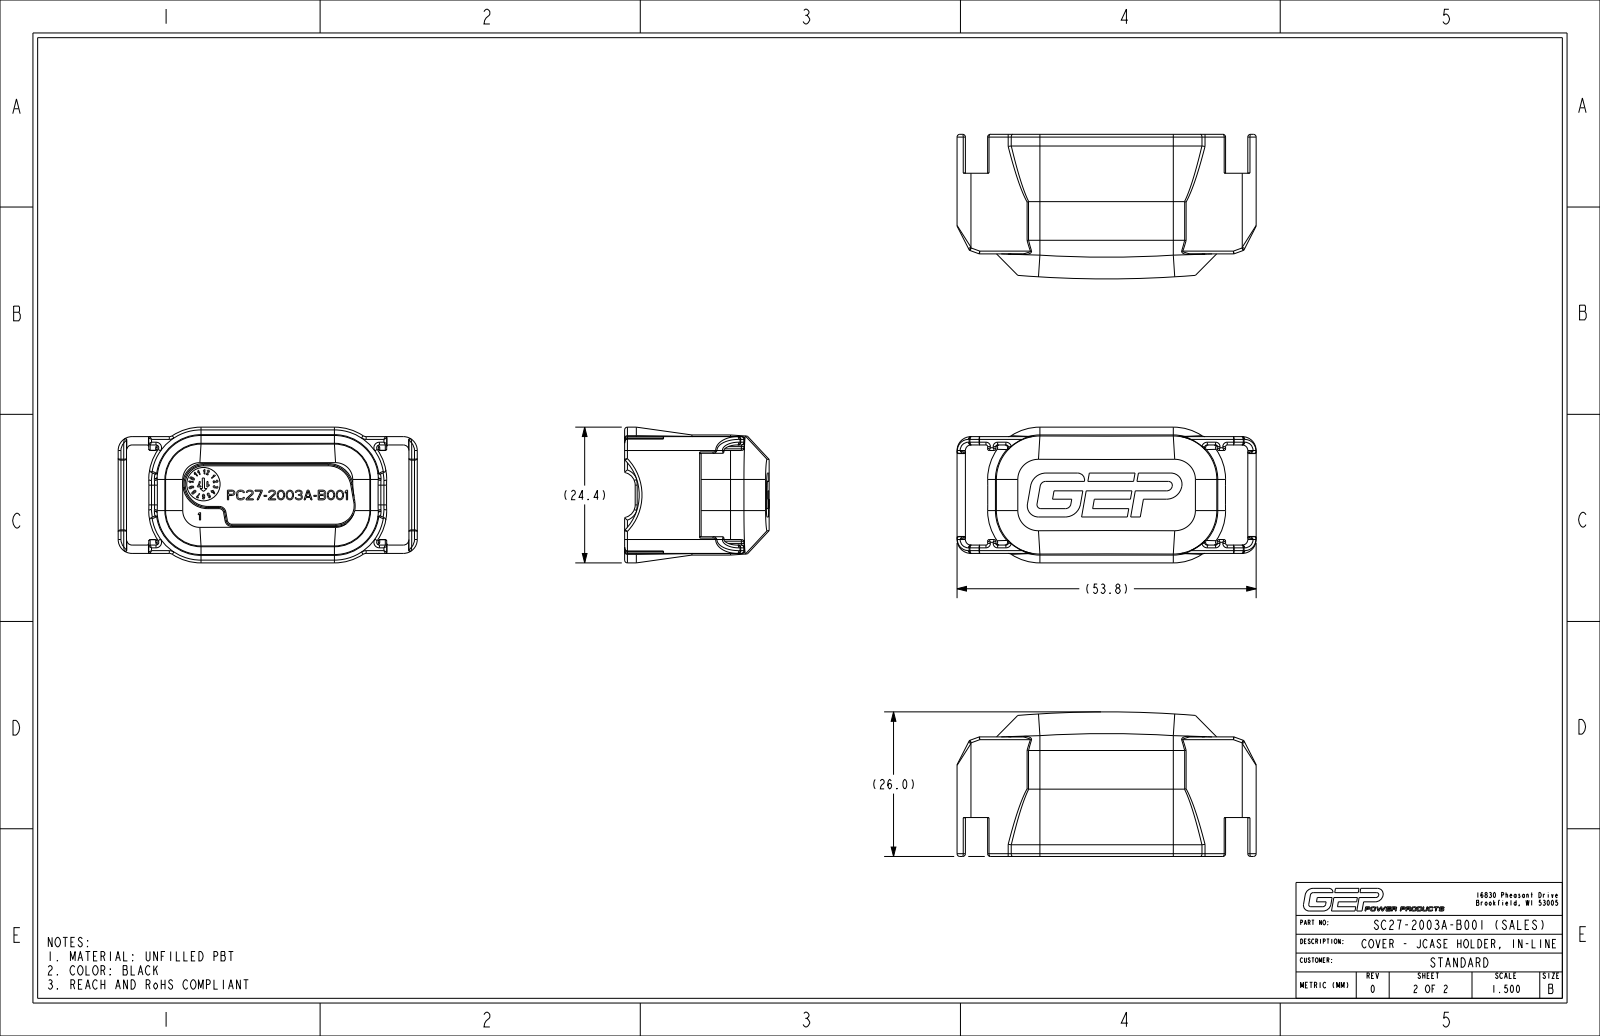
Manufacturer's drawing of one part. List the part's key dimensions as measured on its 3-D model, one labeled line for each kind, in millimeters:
Part name (STEP PRODUCT): PC27-2003A-B001_NCF; SC27-2003A-B001_NCF_ASM
STEP written by: CREO PARAMETRIC BY PTC INC, 2017110 (CONFIG_CONTROL_DESIGN)
Units: millimetres
Bodies: 1 solid, 1434 faces (588 planar, 284 cylindrical, 562 other)
Overall size (bounding box): 53.9 × 26 × 24.41
Volume: 6 574 mm³ · Surface area: 8 865 mm²
Partial cylindrical surfaces — rounded edges, fillets, slot ends (radius × count): R0.5 ×60, R0.25 ×38, R1 ×17, R0.3 ×16, R2.5 ×4, R6.5 ×4, R7.91 ×4, R8 ×4
Main face-to-face distances: 1.5, 19.8, 52.32, 1.2, 21.3, 20.1, 21, 1.8, 18.3, 19.5
